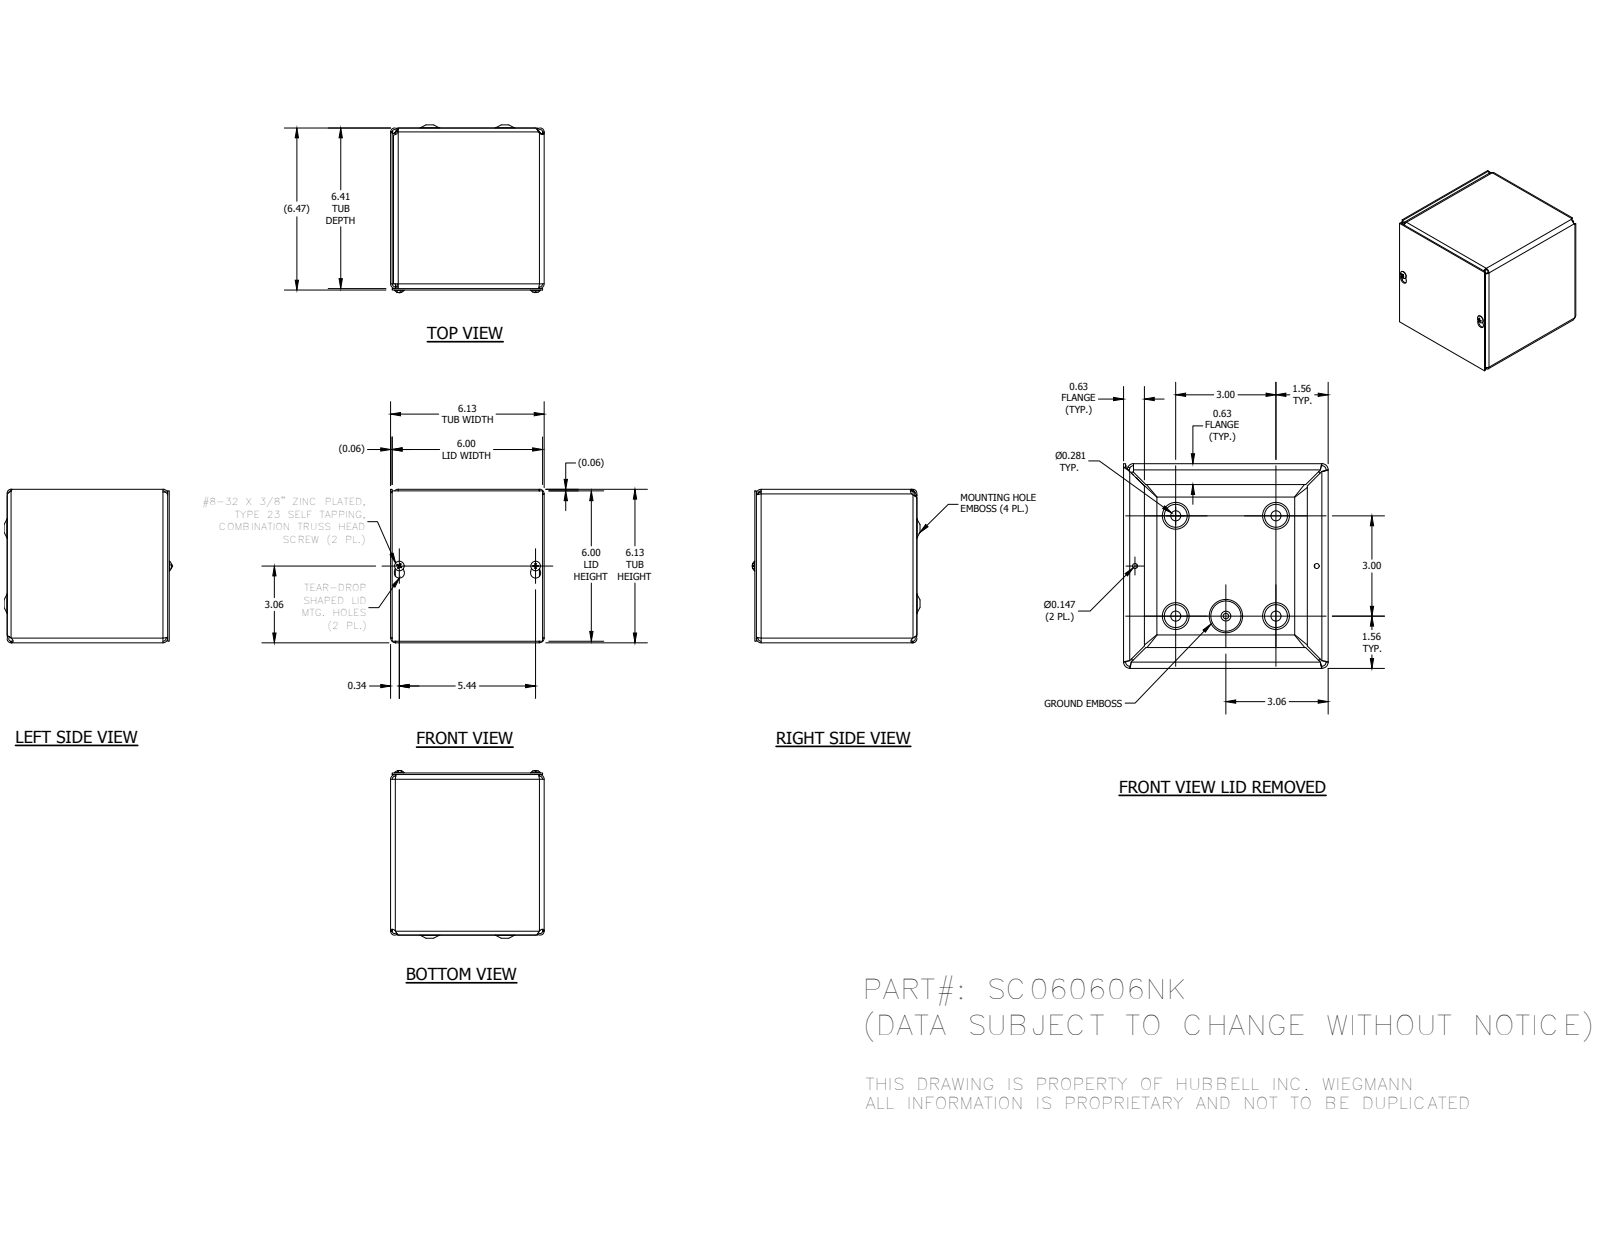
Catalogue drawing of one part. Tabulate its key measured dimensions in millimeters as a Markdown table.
| quantity | value |
| --- | --- |
| part name | SC0606BKP; SC060606NKWRA; SC0606LID; 34056 (+1 more) |
| STEP written by | Autodesk Inventor 2014 (AUTOMOTIVE_DESIGN) |
| units | millimeters |
| bodies | 5 solids, 293 faces (108 planar, 57 cylindrical, 128 other) |
| overall size | 170 × 155.57 × 155.57 |
| volume | 256 337 mm³ |
| surface area | 330 609 mm² |
| round holes (diameter × count) | 7.62 × 4, 3.73 × 2, 4.19 × 1 |
| round bosses / shafts (diameter × count) | 9.75 × 2, 4.17 × 2, 5.8 × 1 |
| partial cylindrical surfaces (radius × count) | 3.17 × 10, 4.75 × 8, 1.4 × 4, 1.57 × 4, 2.38 × 4, 2.97 × 4, 3.15 × 4, 3.96 × 4 |
| main face-to-face distances | 1.57, 154, 152.43, 161.12, 1.58, 162.69, 155.57, 155.58, 154.01, 1.59 |
| hole center spacings | 49.09, 76.2, 38.1, 85.19, 107.76, 113.72, 113.73, 78.86 |
